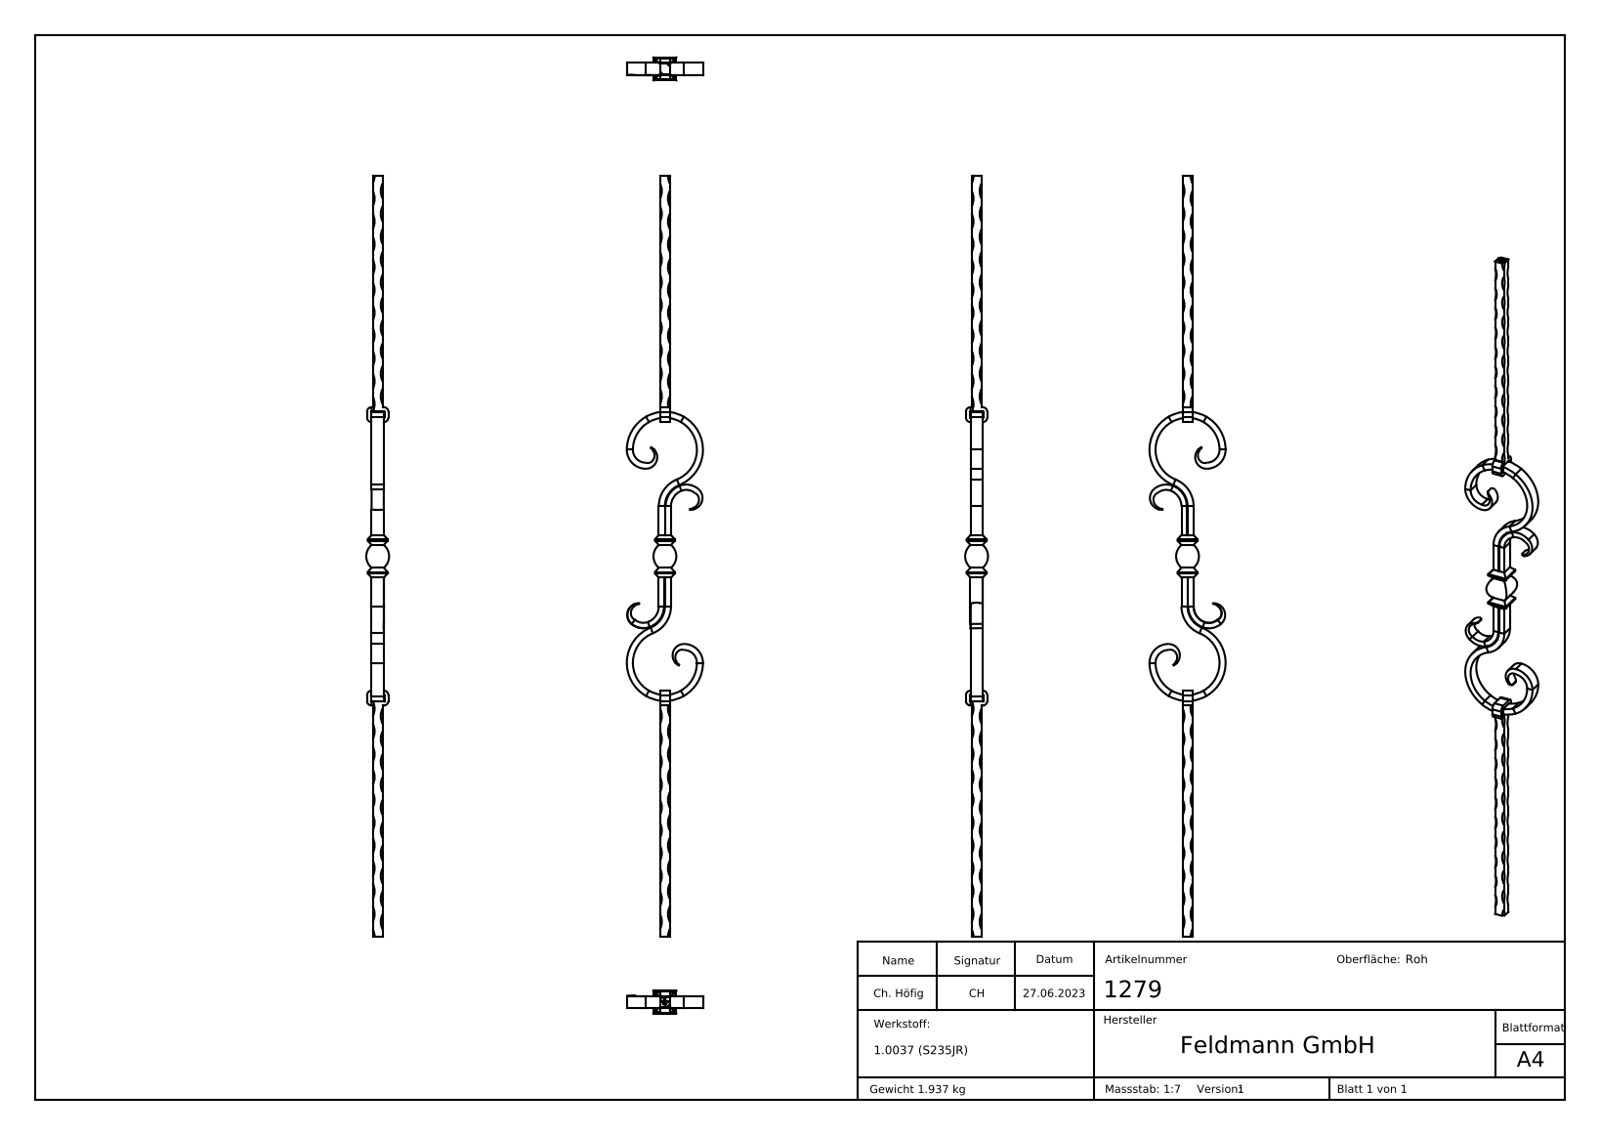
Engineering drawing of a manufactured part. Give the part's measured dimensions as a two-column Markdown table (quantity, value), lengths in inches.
| quantity | value |
| --- | --- |
| part name | 1279 |
| STEP written by | SolidWorks 2018 (CONFIG_CONTROL_DESIGN) |
| units | inches |
| bodies | 3 solids, 452 faces (215 planar, 50 cylindrical, 187 other) |
| overall size | 39.37 × 3.937 × 1.181 |
| volume | 15.15 in³ |
| surface area | 132.4 in² |
| partial cylindrical surfaces (radius × count) | 0.039 × 8, 0.236 × 8, 0.197 × 6, 0.77 × 4, 0.667 × 2, 0.98 × 2, 1.183 × 2, 1.496 × 2 |
| main face-to-face distances | 0.059, 0.571, 0.512, 0.63, 0.197, 0.811, 1.139, 0.276, 0.313, 0.254 |
